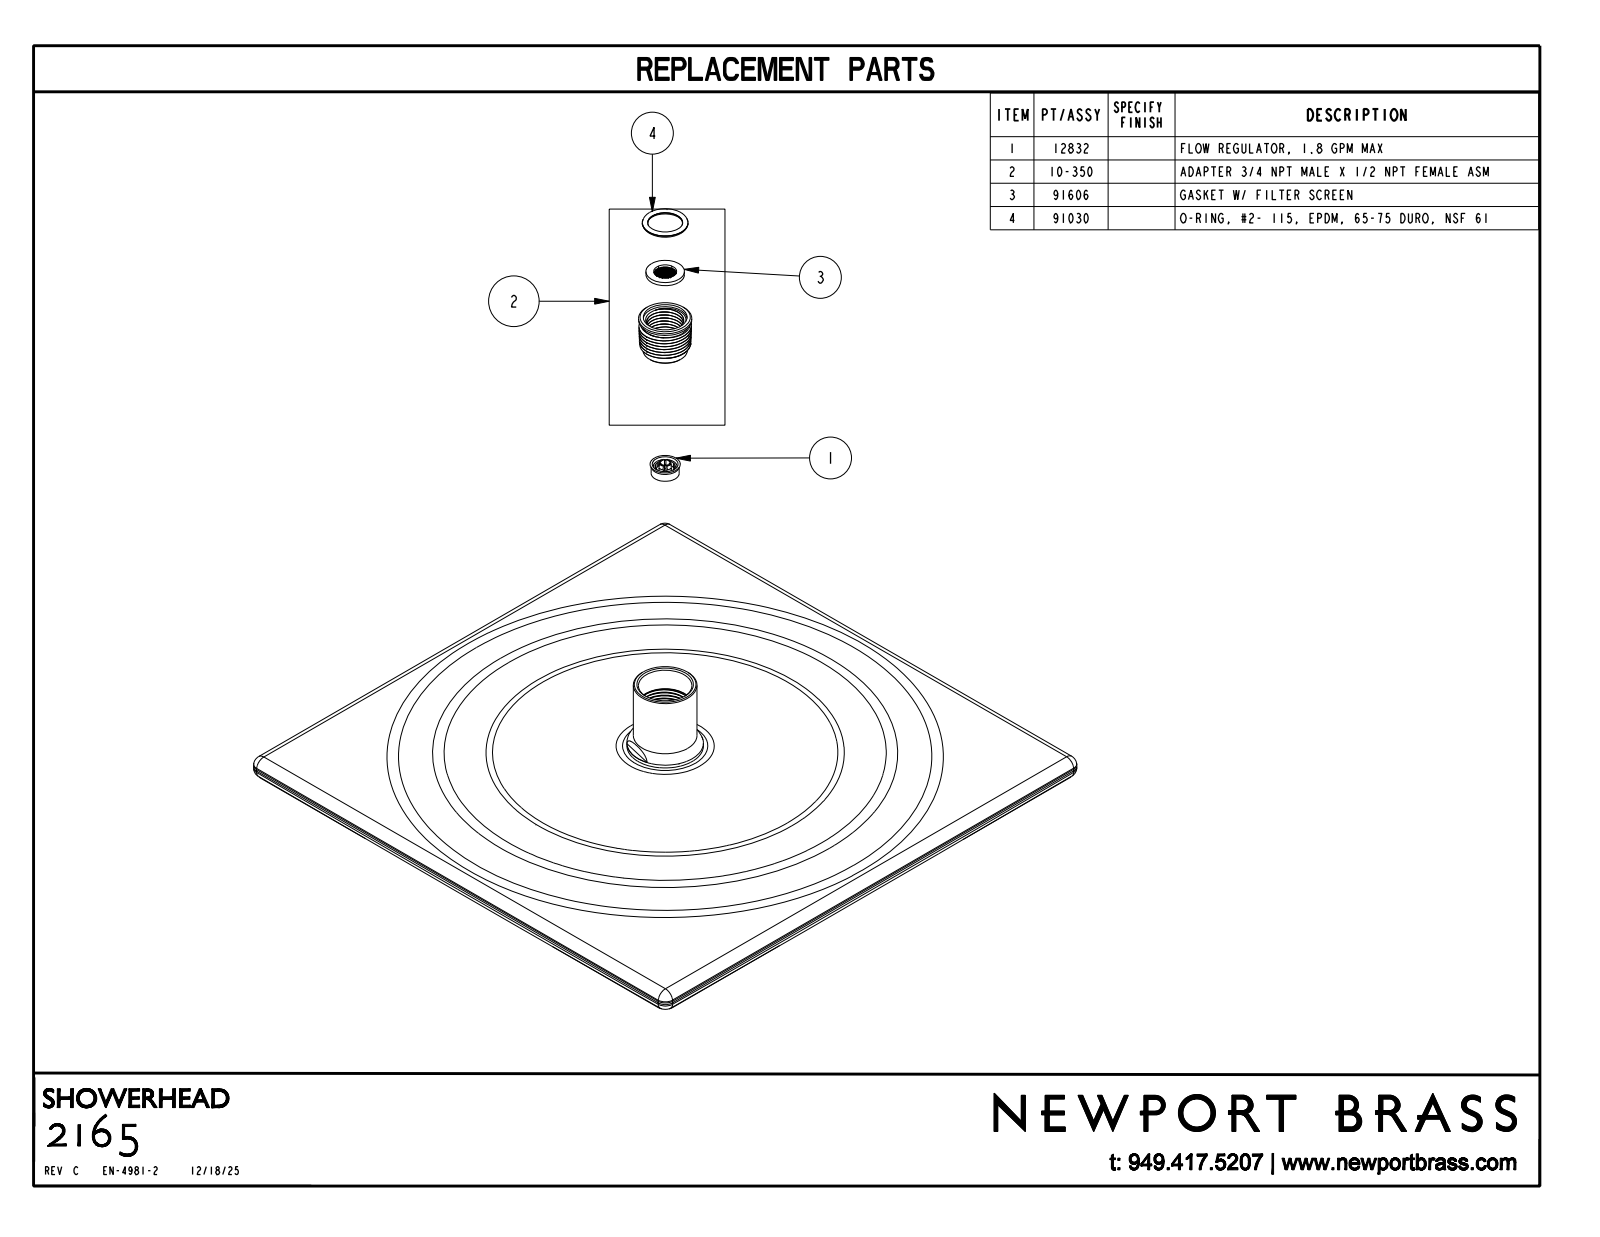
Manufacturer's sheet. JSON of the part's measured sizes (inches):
{"part_name": "2165", "step_written_by": "CREO PARAMETRIC BY PTC INC, 2023134 (CONFIG_CONTROL_DESIGN)", "units": "inches", "bodies": {"solids": 1, "faces": 2984, "planar": 760, "cylindrical": 1112, "other": 1112}, "overall_size": [11.556, 11.556, 2.327], "volume_in3": 80.68, "surface_area_in2": 305.9, "round_holes": [[0.087, 180], [0.16, 180]], "round_bosses_or_shafts": [[0.142, 180], [1.502, 1], [1.25, 1]], "partial_cylinders_radius": [[0.2, 14], [0.05, 4], [0.158, 4]], "face_to_face_distances": [0.516, 0.618, 0.102, 11.555, 0.05, 0.466, 2.259, 1.743, 1.641, 0.068], "hole_center_spacings": [1.1, 1.78, 0.895, 1.515, 0.578, 0.578, 0.579, 1.099]}
